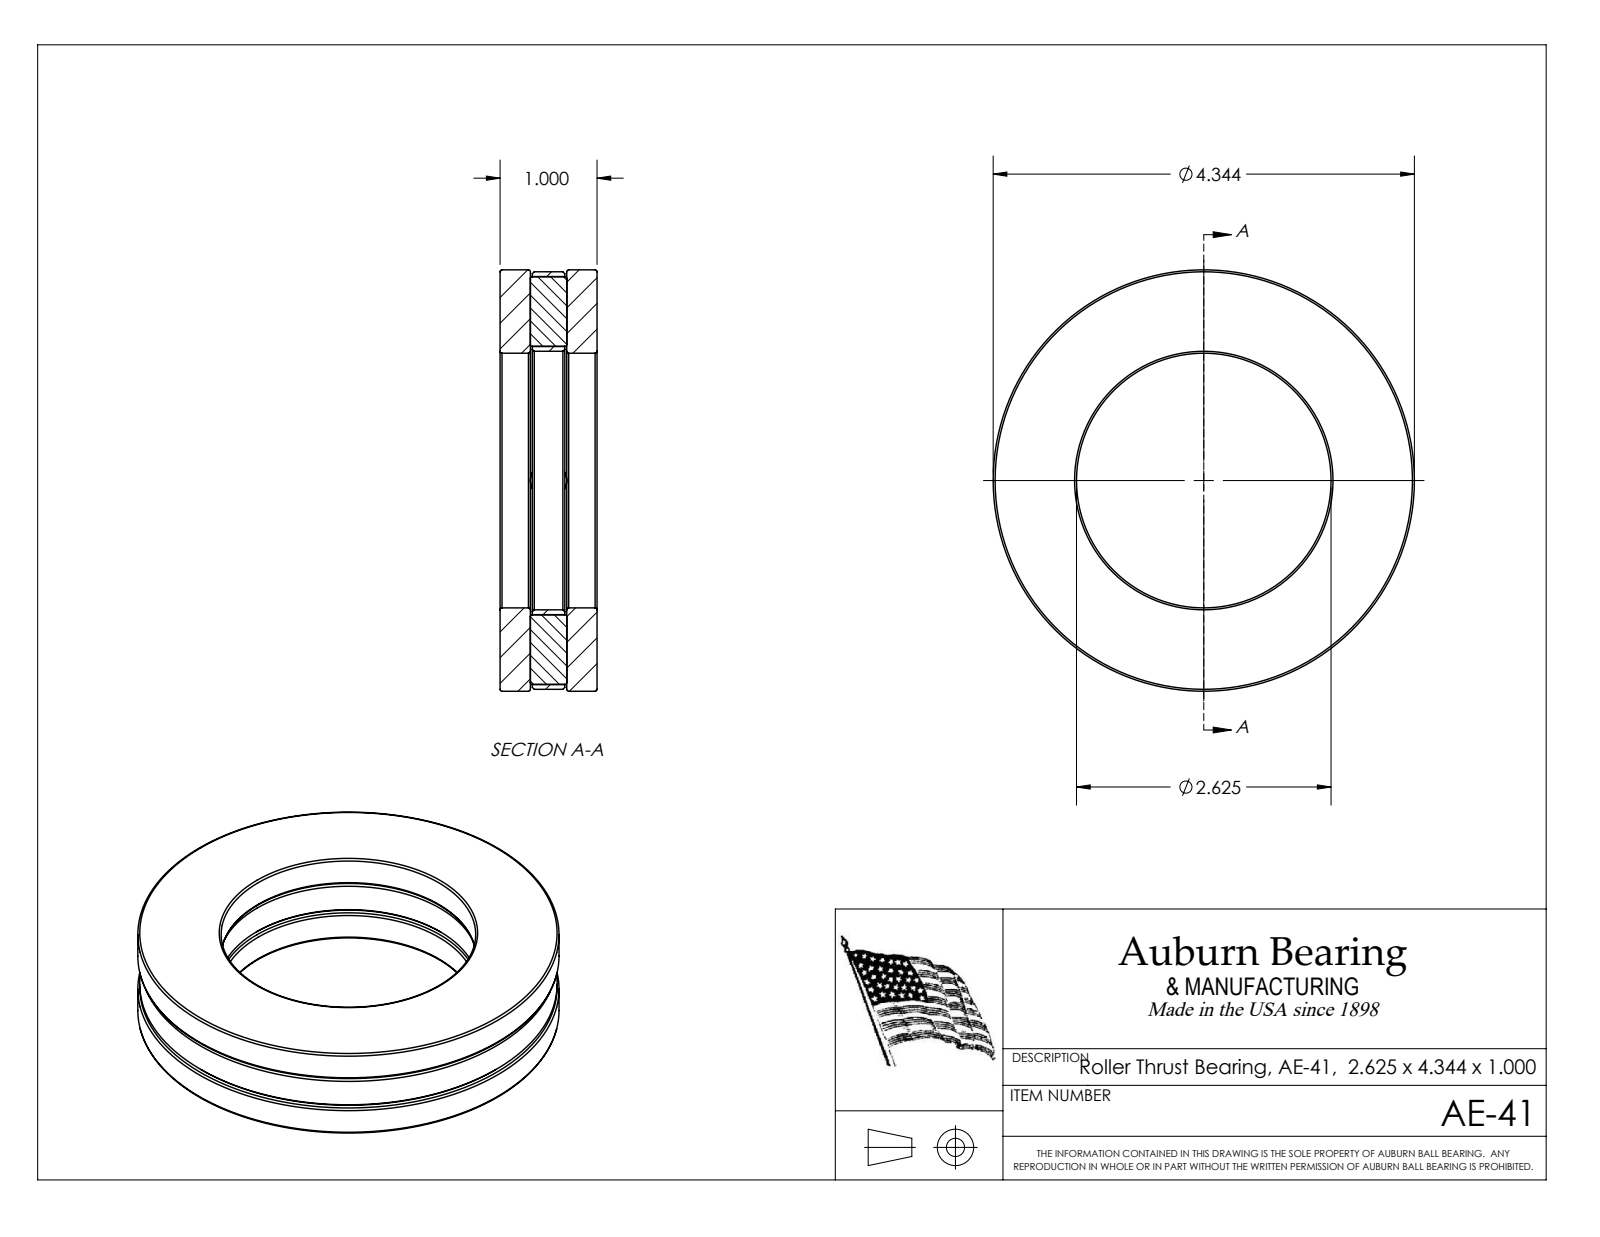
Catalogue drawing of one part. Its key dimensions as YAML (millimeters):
part_name: "AE-41"
step_written_by: "SolidWorks 2017 (CONFIG_CONTROL_DESIGN)"
units: millimeters
bodies: {solids: 7, faces: 60, planar: 30, cylindrical: 10, other: 20}
overall_size: [110.3, 110.3, 25.4]
volume: 144600
surface_area: 51800
round_holes:
  - {diameter: 66.7, count: 1}
  - {diameter: 67.7, count: 1}
round_bosses_or_shafts:
  - {diameter: 9.5, count: 2}
  - {diameter: 110.3, count: 1}
  - {diameter: 109.3, count: 1}
face_to_face_distances: [8, 17.4, 8.5, 16.9, 0.5, 9, 9.5, 25.4, 8.5, 30.4]
